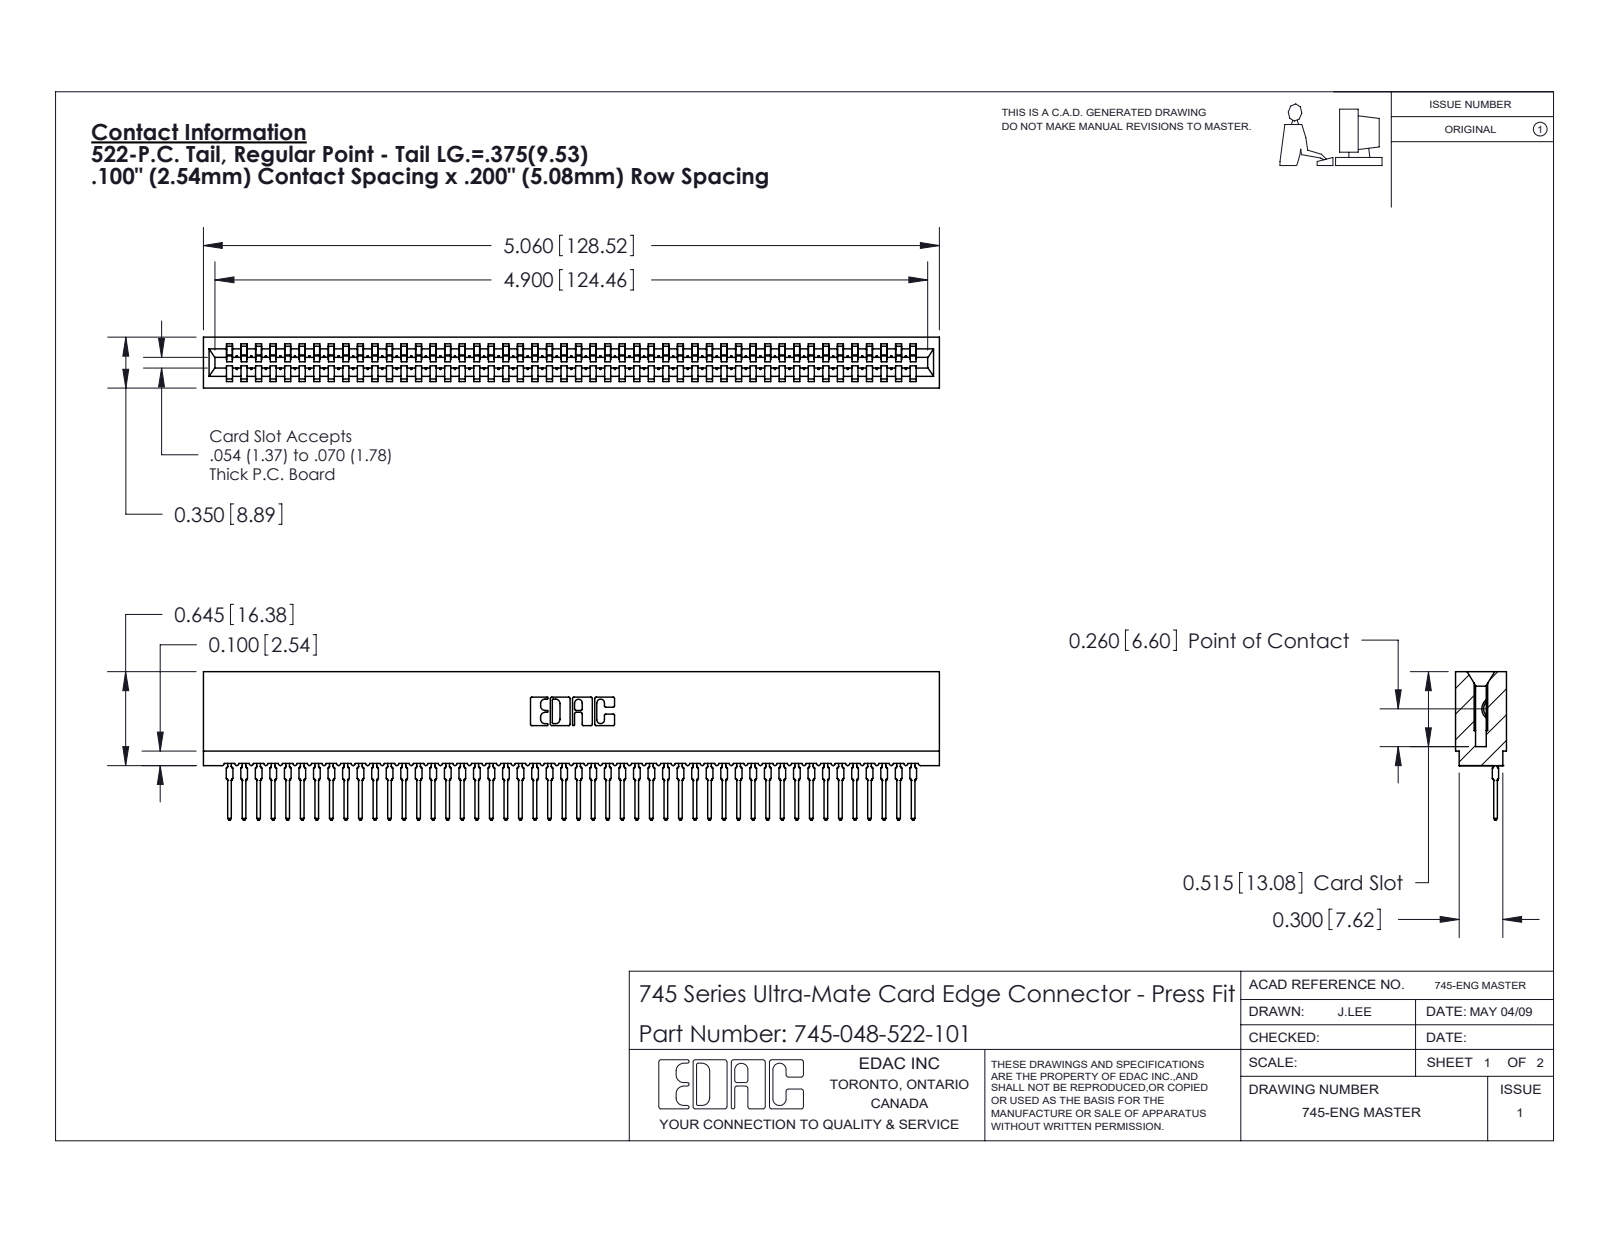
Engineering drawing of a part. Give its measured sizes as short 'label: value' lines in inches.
name: 745-048-522-101; 745 Part_Insulator Option - 01; 745-292-001_522
written by: SolidWorks 2020 (CONFIG_CONTROL_DESIGN)
unit: in
bodies: 49 solids, 5471 faces (3271 planar, 952 cylindrical, 1248 other)
size: 5.06 × 1.021 × 0.35
volume: 0.679 in³; area: 32.49 in²
rounds: 96× R0.015, 96× R0.021, 22× R0.01, 6× R0.007, 6× R0.031, 4× R0.005, 4× R0.011, 3× R0.026
face distances: 0.35, 0.045, 0.305, 0.138, 0.212, 0.093, 0.167, 0.063, 0.287, 0.243
